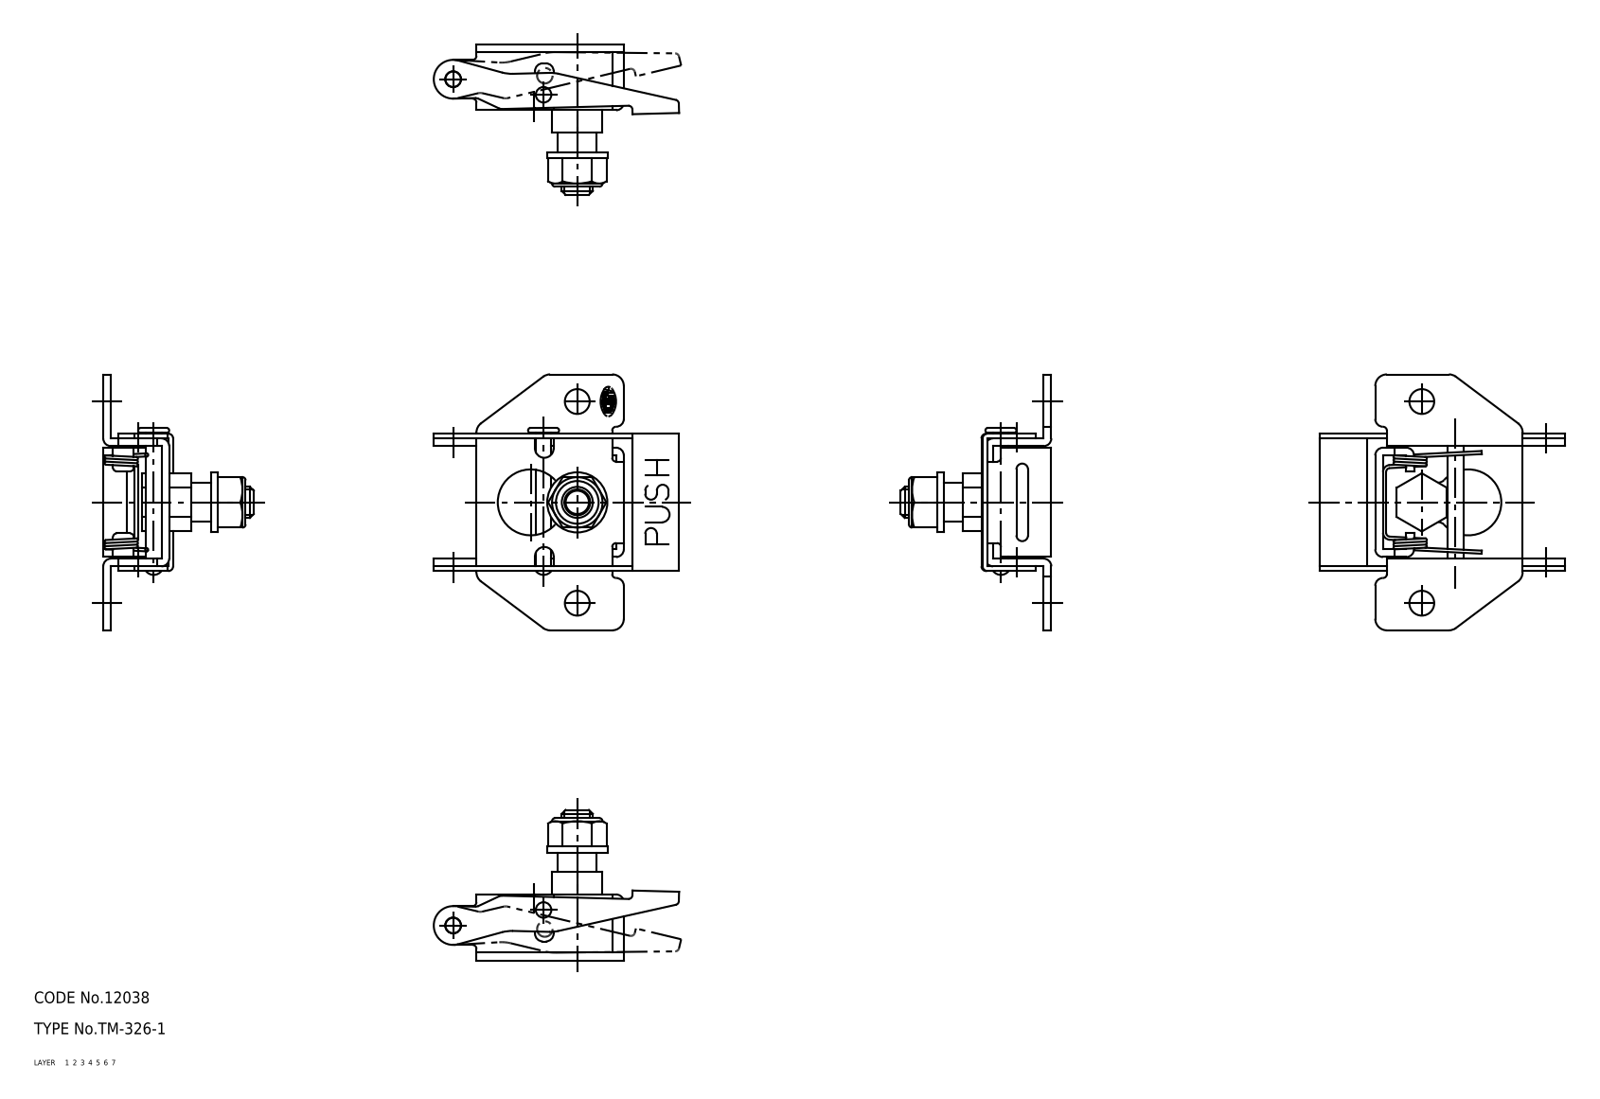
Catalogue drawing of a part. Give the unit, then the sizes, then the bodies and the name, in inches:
Units: inches
Overall size (bounding box): 2.598 × 2.489 × 1.528
Round holes (diameter × count): ⌀0.252 ×2, ⌀0.157 ×1, ⌀0.161 ×1, ⌀0.433 ×1
Round bosses / shafts (diameter × count): ⌀0.031 ×5, ⌀0.61 ×1, ⌀0.39 ×1, ⌀0.315 ×1, ⌀0.157 ×1
Partial cylindrical surfaces — rounded edges, fillets, slot ends (radius × count): R0.039 ×18, R0.079 ×17, R0.118 ×6, R0.047 ×2, R0.059 ×2, R0.094 ×2, R0.394 ×2, R0.197 ×1
Main face-to-face distances: 0.079, 0.591, 0.047, 0.512, 1.22, 1.299, 1.268, 1.346, 0.126, 0.669
Hole centre spacings: 1.024, 2.047
Volume: 0.759 in³ · Surface area: 21.5 in²
Bodies: 4 solids, 267 faces (115 planar, 118 cylindrical, 34 other)
Part name (STEP PRODUCT): TM_326_1; shaft; lever; base
STEP written by: SolidWorks 2015 (AUTOMOTIVE_DESIGN)
